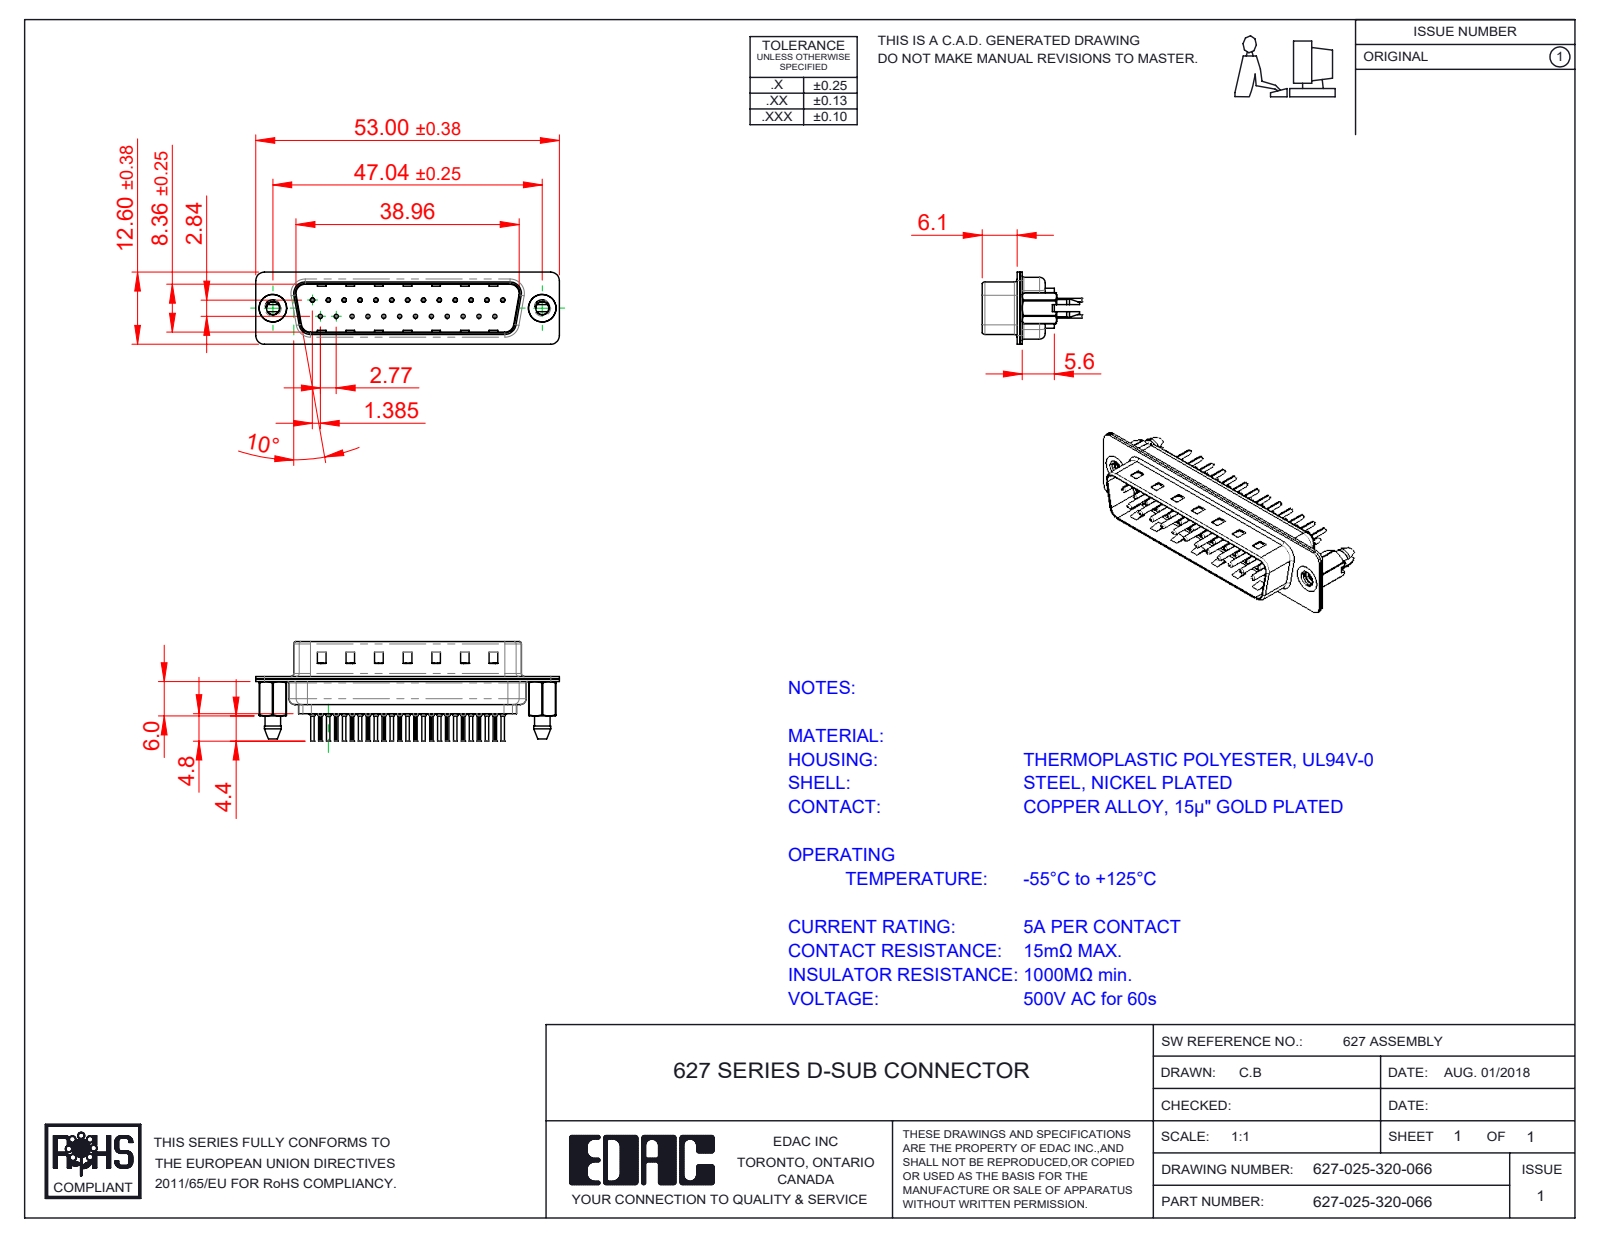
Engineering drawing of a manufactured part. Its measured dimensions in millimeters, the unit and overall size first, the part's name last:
Units: millimetres
Overall size (bounding box): 53 × 17.3 × 12.6
Round holes (diameter × count): ⌀0.2 ×25, ⌀0.35 ×25, ⌀1.1 ×25, ⌀1.6 ×25, ⌀2.26 ×2, ⌀4 ×2, ⌀4.8 ×2
Round bosses / shafts (diameter × count): ⌀2 ×25, ⌀1.5 ×25, ⌀0.75 ×25, ⌀0.6 ×25, ⌀4.9 ×2
Partial cylindrical surfaces — rounded edges, fillets, slot ends (radius × count): R0.1 ×50, R1.5 ×18, R2 ×12, R1.6 ×10, R0.5 ×8, R0.25 ×4, R0.6 ×4, R0.65 ×4
Main face-to-face distances: 0.4, 0.45, 0.82, 9.58, 8.76, 0.9, 1.5, 1.4, 6.5, 6.05
Hole centre spacings: 3.16, 8.31, 2.77, 5.54, 11.08, 16.62, 5.03, 5.04
Volume: 2 797 mm³ · Surface area: 8 096 mm²
Bodies: 30 solids, 2900 faces (803 planar, 1094 cylindrical, 1003 other)
Part name (STEP PRODUCT): 627 Housing_25 LP; 627 Shell Front_25 Contacts; 627 Contact Row 1_20L; 627 Contact Row 2_20L (+3 more)
STEP written by: SolidWorks 2020 (CONFIG_CONTROL_DESIGN)
